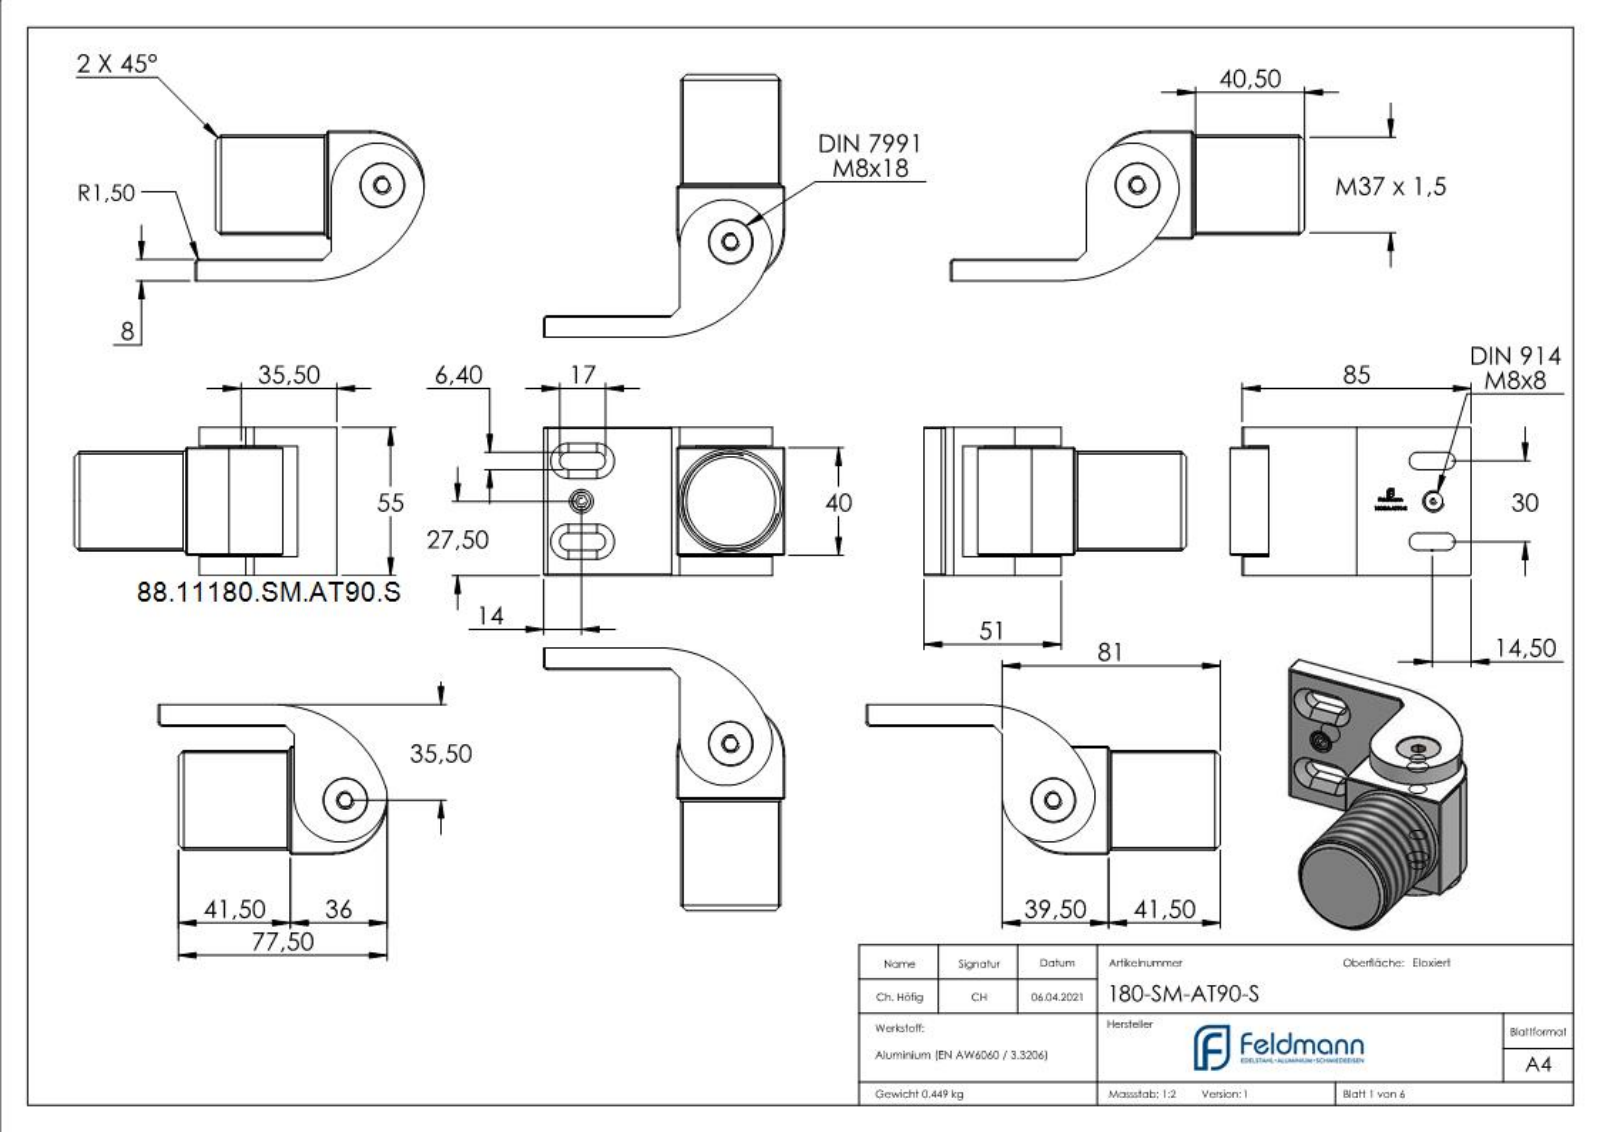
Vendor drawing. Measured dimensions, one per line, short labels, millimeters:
name: DIN-7991 M3-M10; Teil3; Teil1; 180-SM-AT90-S (+8 more)
written by: SolidWorks 2018 (CONFIG_CONTROL_DESIGN)
unit: mm
bodies: 12 solids, 591 faces (241 planar, 88 cylindrical, 262 other)
size: 14000.35 × 5999.86 × 5999.7
volume: 141 365 mm³; area: 41 751 mm²
holes: 2× ⌀6.8, 1× ⌀8.5, 1× ⌀16.5, 1× ⌀19, 1× ⌀23.6, 1× ⌀26
bosses: 2× ⌀8, 1× ⌀37, 1× ⌀23.4, 1× ⌀18.8, 1× ⌀16
rounds: 12× R0.5, 4× R3.2, 1× R1.5, 1× R10, 1× R17.25, 1× R20, 1× R44.11
face distances: 48, 7, 6.5, 8, 41.5, 0.5, 55, 7.5, 47.5, 40.5
